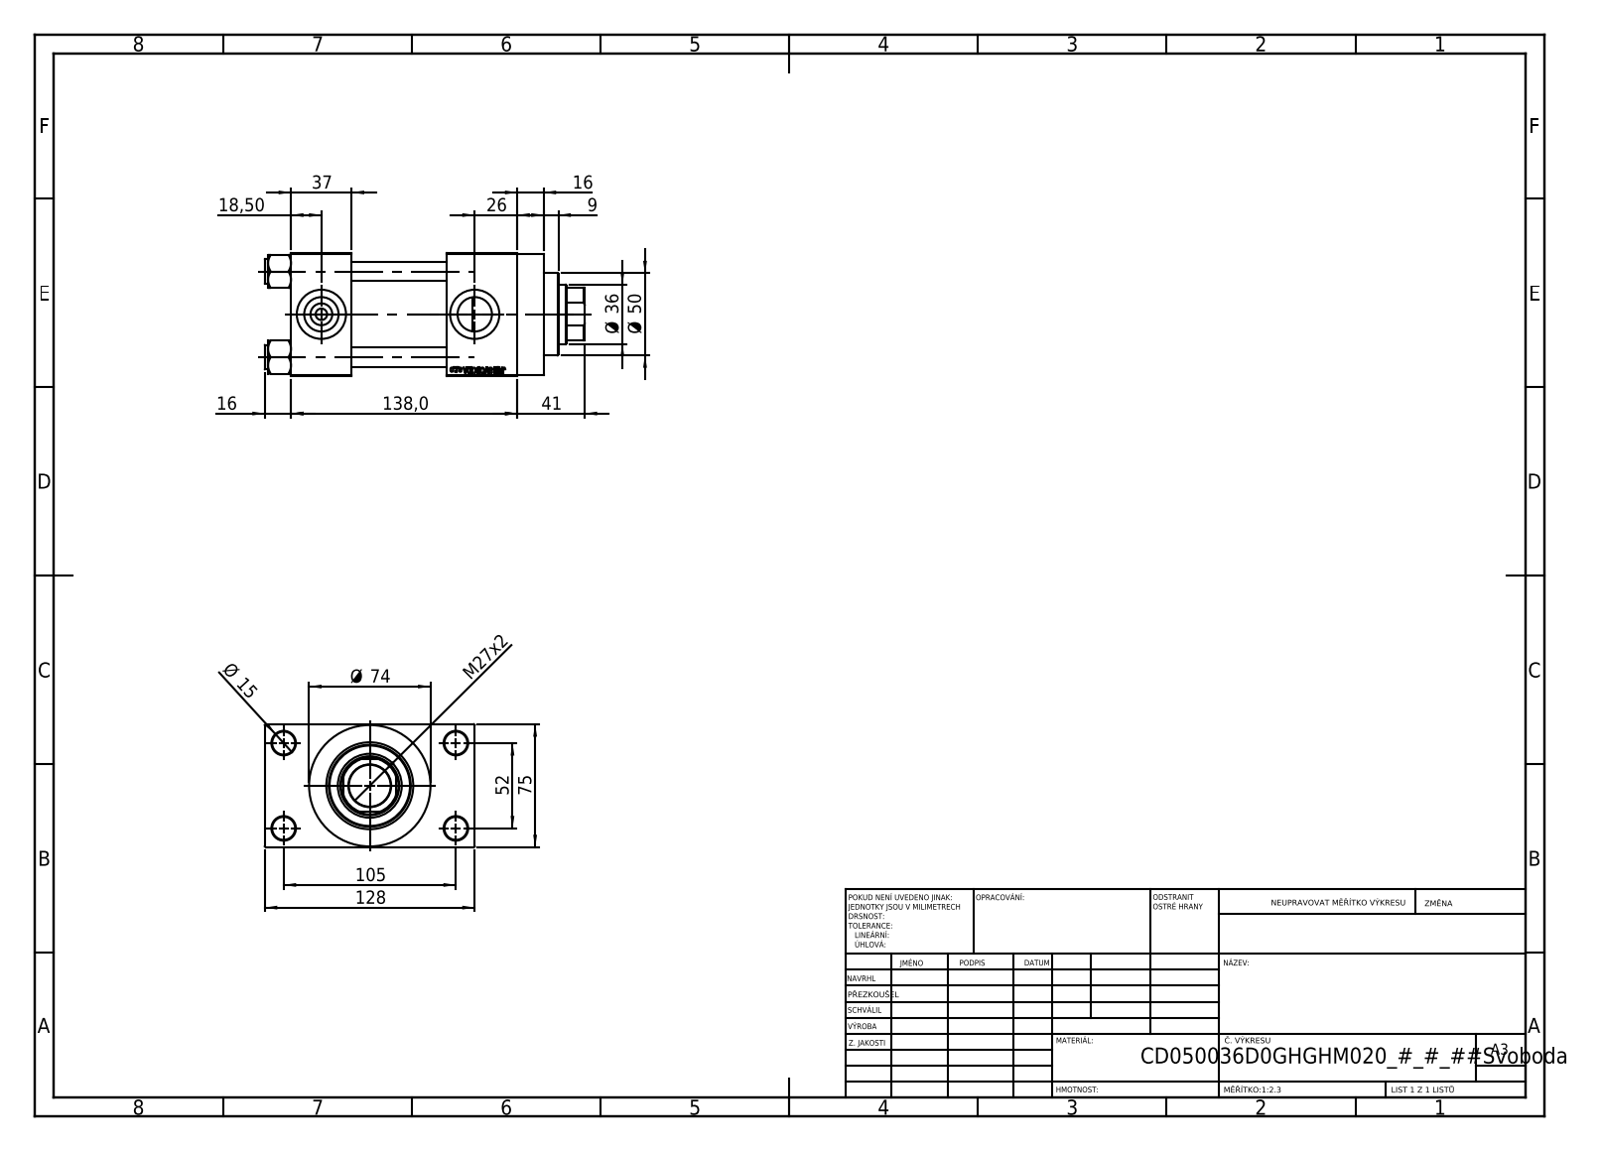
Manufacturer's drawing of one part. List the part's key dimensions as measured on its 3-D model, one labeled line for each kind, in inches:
Part name (STEP PRODUCT): V215CD_D_TYCINKA; V215CD_VC_A; V215CD_NUT_M5_D; V215CD_VCP_D (+1 more)
STEP written by: SolidWorks 2019 (CONFIG_CONTROL_DESIGN)
Units: inches
Bodies: 11 solids, 1103 faces (497 planar, 88 cylindrical, 518 other)
Overall size (bounding box): 7.677 × 5.039 × 2.953
Volume: 49.88 in³ · Surface area: 272.1 in²
Round holes (diameter × count): ⌀0.472 ×4, ⌀0.551 ×4, ⌀0.276 ×2, ⌀0.825 ×2, ⌀1.181 ×2, ⌀1.004 ×1, ⌀1.417 ×1, ⌀1.535 ×1, ⌀1.614 ×1, ⌀2.087 ×1
Round bosses / shafts (diameter × count): ⌀0.591 ×4, ⌀2.913 ×1, ⌀2.205 ×1, ⌀1.969 ×1
Partial cylindrical surfaces — rounded edges, fillets, slot ends (radius × count): R0.689 ×1
Main face-to-face distances: 2.953, 2.283, 1.457, 3.74, 1.043, 1.693, 5.433, 3.976, 3.996, 0.63
Hole centre spacings: 1.037, 1.456, 2.059, 2.3, 2.307, 3.096, 3.715, 2.047
